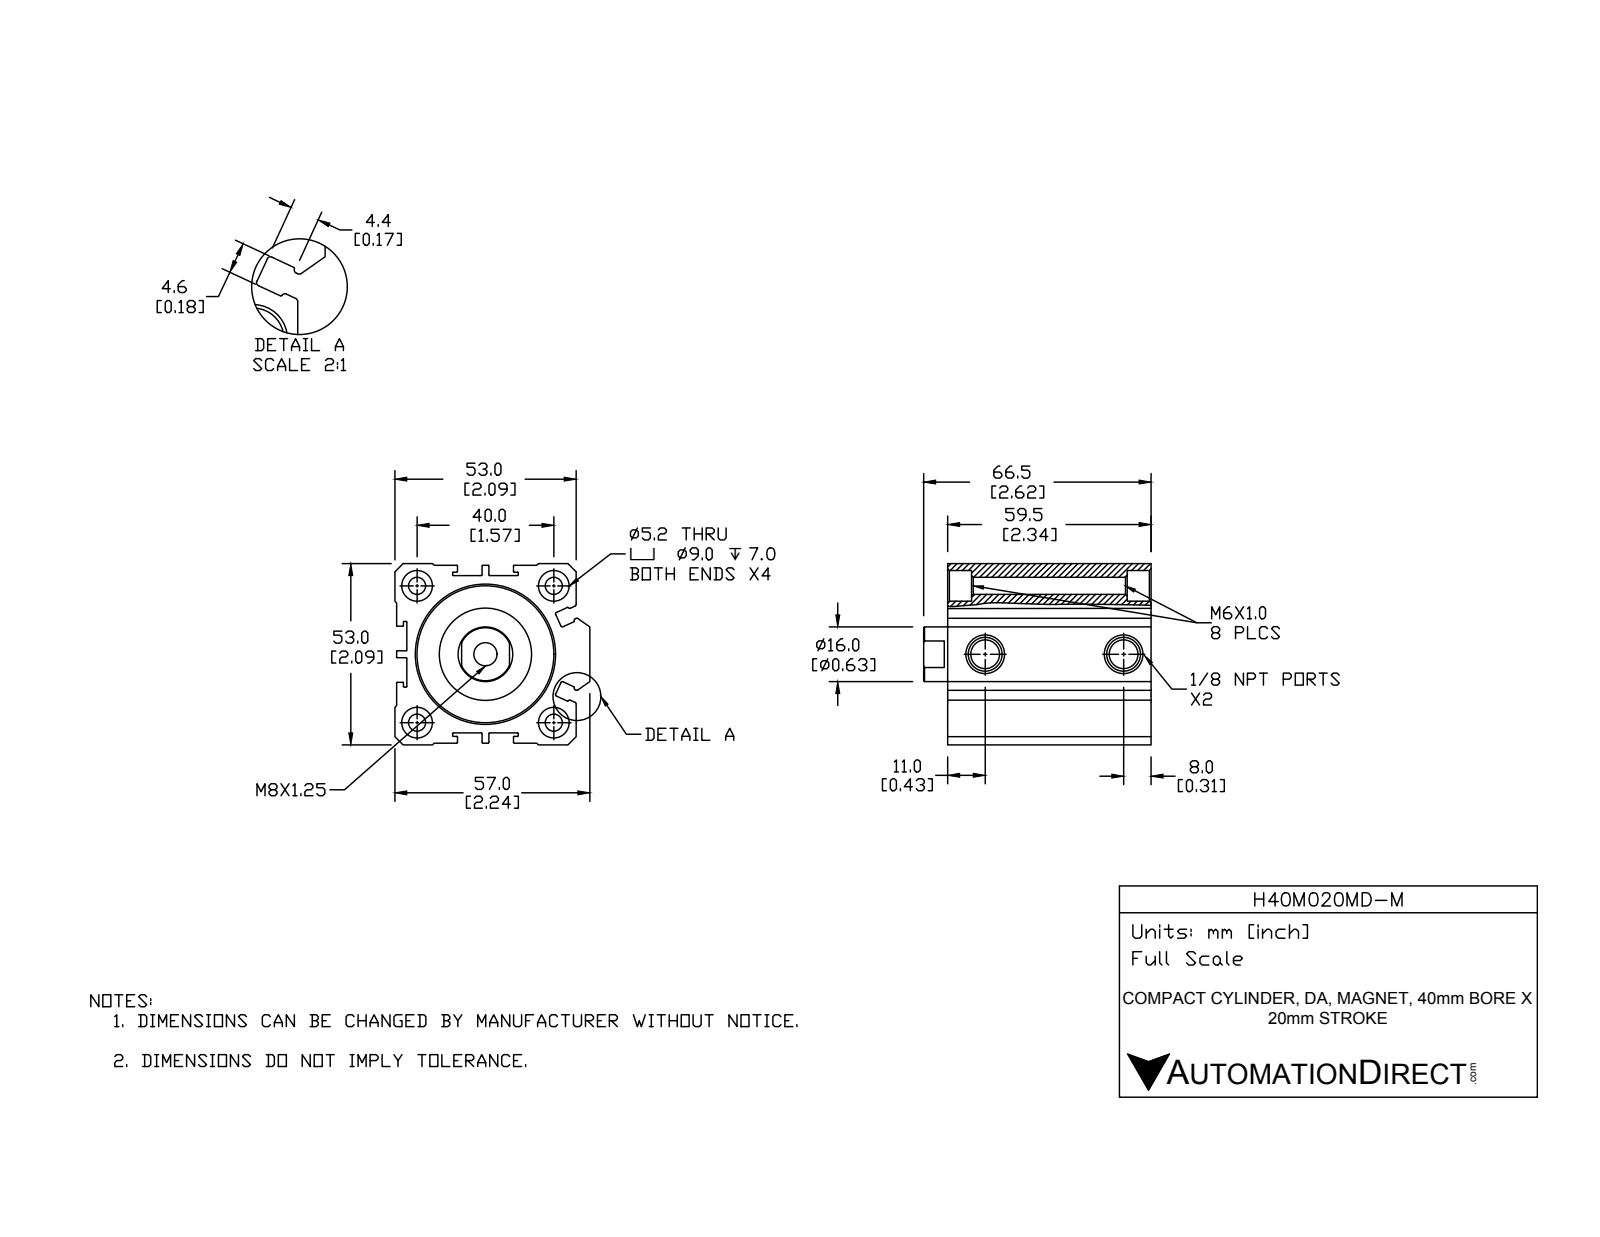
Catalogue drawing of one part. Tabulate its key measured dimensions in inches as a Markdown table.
| quantity | value |
| --- | --- |
| part name | H40M020MD-M-PISTON; H40M020MD-M-BODY; H40M020MD-M |
| STEP written by | SolidWorks 2015 (CONFIG_CONTROL_DESIGN) |
| units | inches |
| bodies | 2 solids, 255 faces (99 planar, 103 cylindrical, 53 other) |
| overall size | 2.618 × 2.244 × 2.087 |
| volume | 7.42 in³ |
| surface area | 67.39 in² |
| round holes (diameter × count) | 0.197 × 4, 0.354 × 4, 0.332 × 2, 0.268 × 1, 0.63 × 1, 1.161 × 1, 1.575 × 1 |
| round bosses / shafts (diameter × count) | 1.063 × 1, 0.984 × 1 |
| partial cylindrical surfaces (radius × count) | 0.008 × 40, 0.02 × 12 |
| main face-to-face distances | 0.138, 1.949, 2.067, 0.02, 0.118, 2.087, 1.929, 2.343, 2.146, 0.839 |
| hole center spacings | 1.113, 1.575, 2.227, 1.594 |
